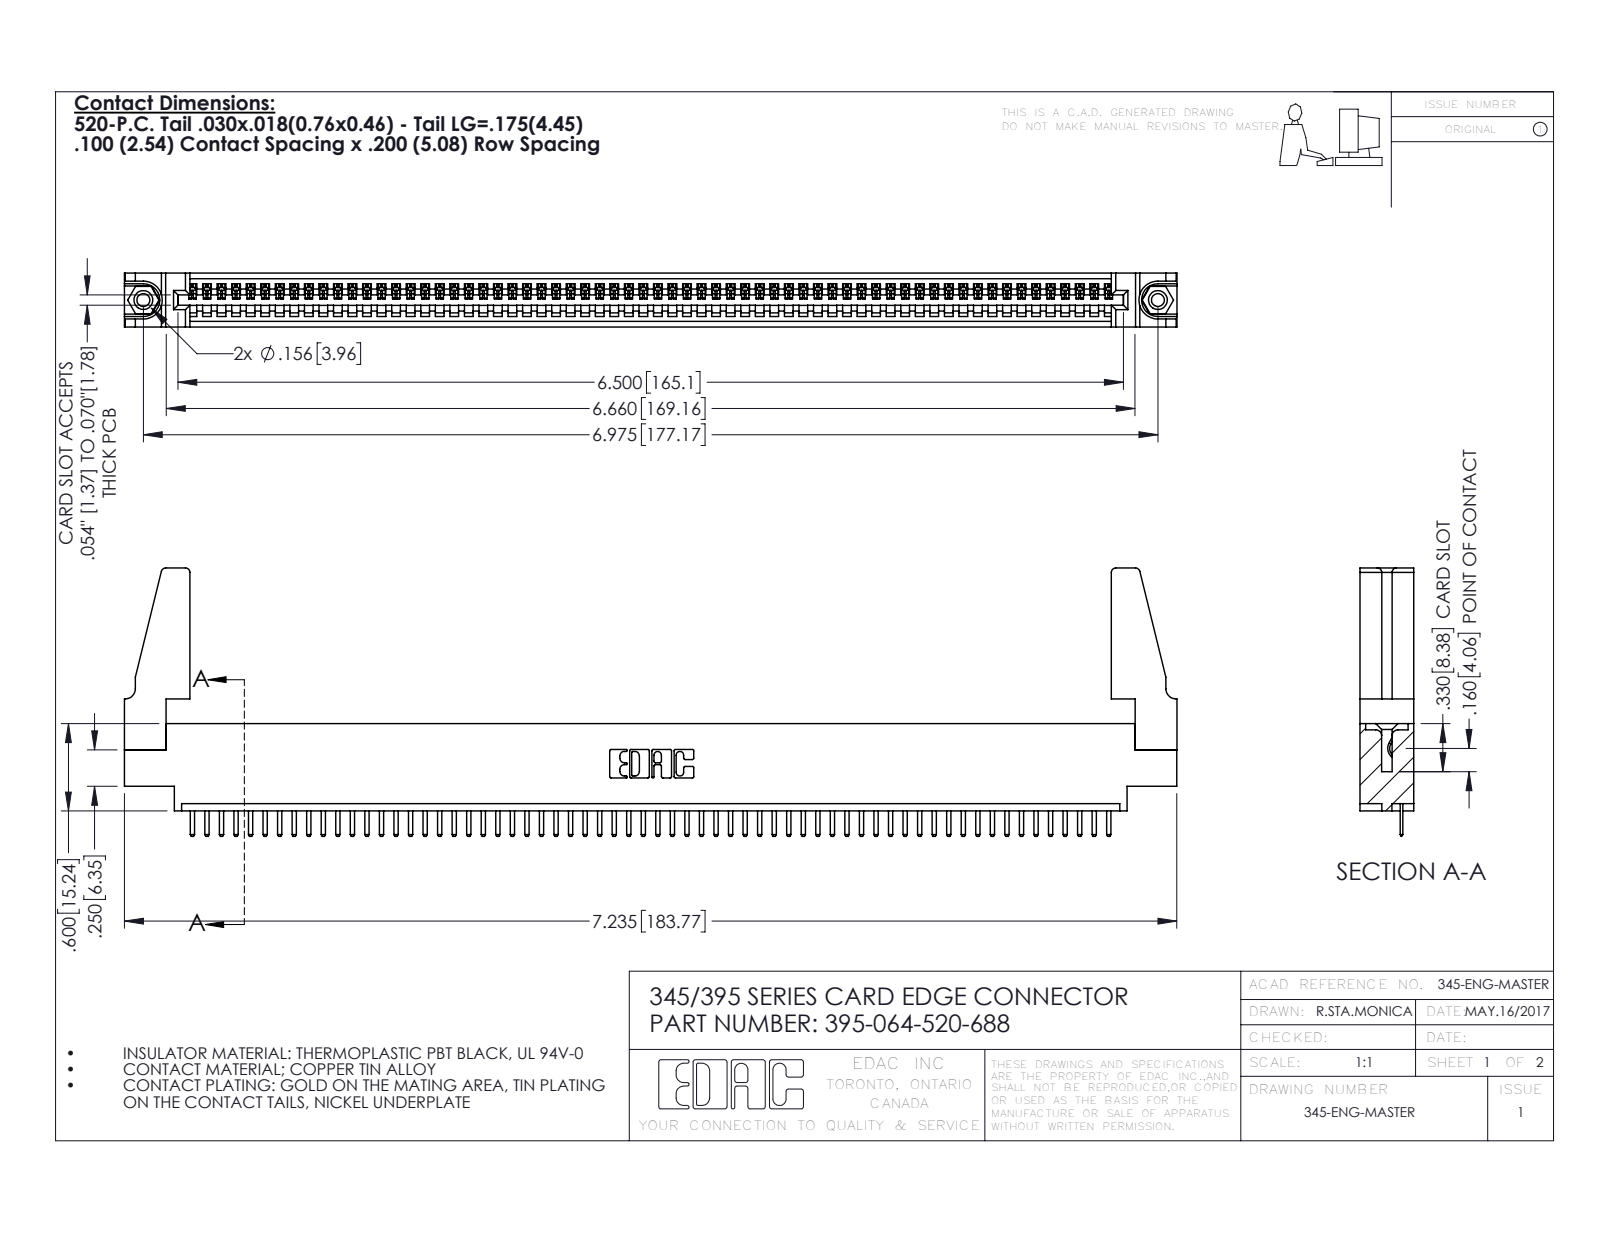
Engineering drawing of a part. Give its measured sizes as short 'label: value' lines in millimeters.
name: 345-292-001_345-293-120; 345 Part_0.170 Offset - 0.156 Dia-TH; 395-064-520-688; 345-250-001_345-250-001-102 (+1 more)
written by: SolidWorks 2016 (CONFIG_CONTROL_DESIGN)
unit: mm
bodies: 69 solids, 4222 faces (2844 planar, 1362 cylindrical, 16 other)
size: 183.8 × 46.9 × 9.4
volume: 20 600 mm³; area: 25 990 mm²
holes: 2× ⌀2.3, 2× ⌀3.2, 2× ⌀4, 1× ⌀1.6
bosses: 2× ⌀3.9
rounds: 130× R0.3, 128× R0.2, 22× R0.3, 8× R0.8, 6× R0.2, 6× R0.8, 3× R0.7, 2× R0.8
face distances: 1.8, 9.4, 7.6, 2.5, 6.9, 0.6, 5.1, 5.7, 1.8, 4.4
hole spacings: 6.9, 171.2, 177.2
